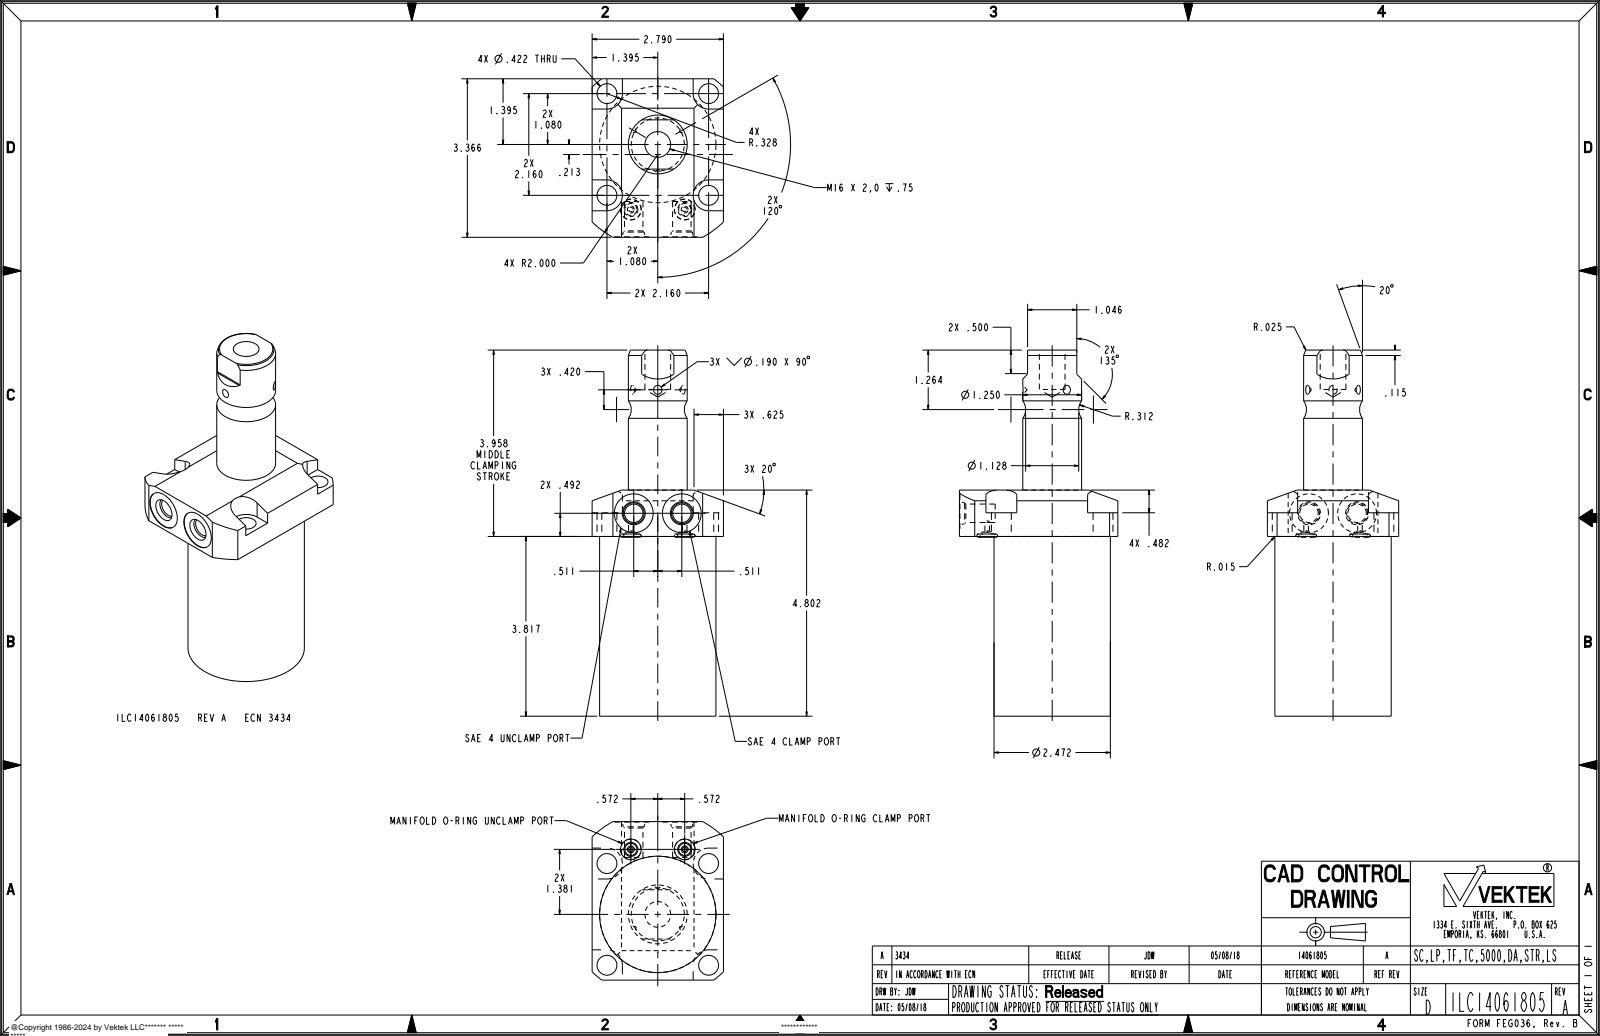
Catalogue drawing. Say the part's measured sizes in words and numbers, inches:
The part is named "ILC14061805". Its 3-D file was written by "PRO/ENGINEER BY PARAMETRIC TECHNOLOGY CORPORATION, 2013320 (AUTOMOTIVE_DESIGN)". It is 3 solids with 119 faces: 37 planar, 46 cylindrical and 36 other. Overall it measures 7.775 by 3.366 by 2.79 inches. Its volume is 29.13 cubic inches and its surface area 75.99 square inches. Round holes: 4 of diameter 0.422, 2 of diameter 0.098, 2 of diameter 0.256, 2 of diameter 0.392, 2 of diameter 0.438, 2 of diameter 0.825, 1 of diameter 0.546. Round bosses or shafts: 1 of diameter 2.472, 1 of diameter 1.25. Partial cylindrical surfaces (rounded edges, fillets, slot ends): 4 of radius 0.328, 2 of radius 0.03, 1 of radius 2. The main face-to-face distances are 3.817, 4.802, 0.985, 2.79, 4.32, 0.503, 0.482, 3.366, 7.775, 3.958. The hole center spacings are 1.527, 2.16, 0.591, 1.495, 1.679, 2.513, 2.964, 3.054.
